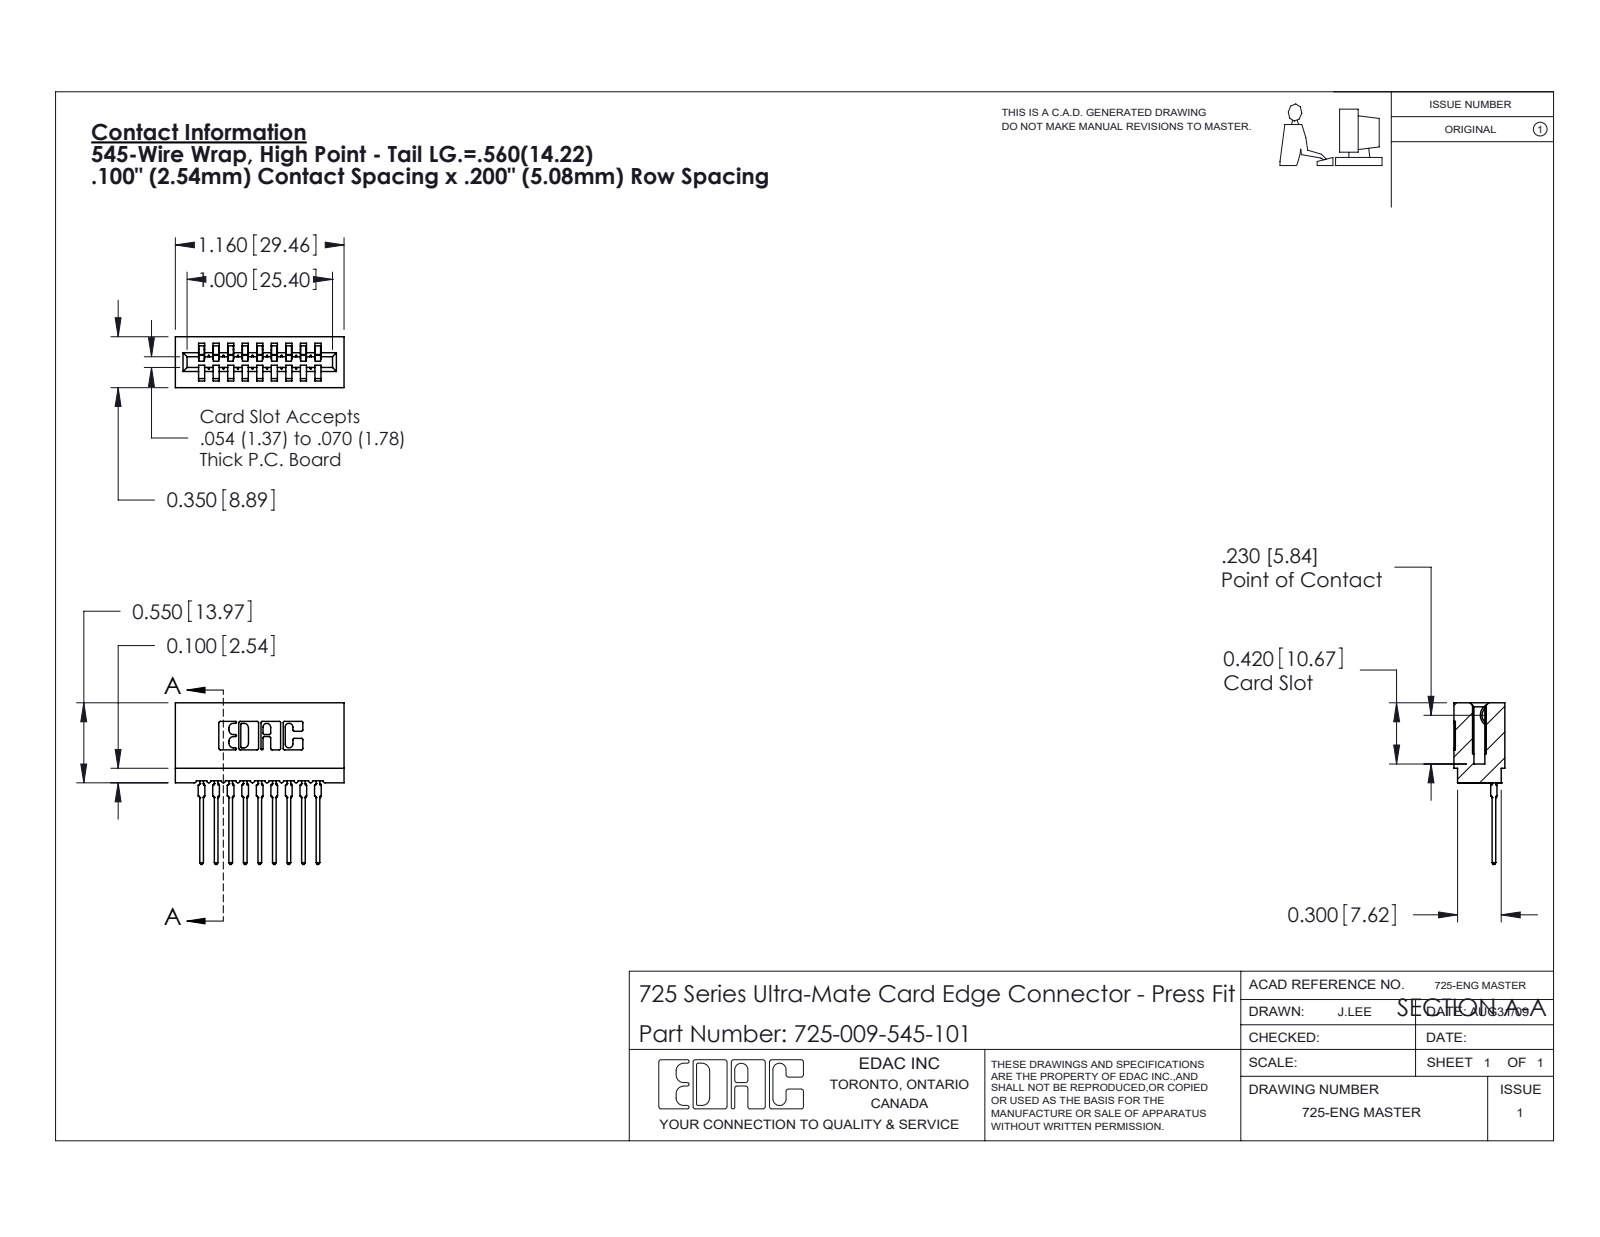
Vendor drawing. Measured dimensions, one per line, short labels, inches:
name: 725-009-545-101; 725 Part_Insulator Option - 01; 745-292-001_545
written by: SolidWorks 2020 (CONFIG_CONTROL_DESIGN)
unit: in
bodies: 10 solids, 1103 faces (658 planar, 211 cylindrical, 234 other)
size: 1.16 × 1.111 × 0.35
volume: 0.149 in³; area: 6.576 in²
rounds: 22× R0.01, 18× R0.015, 18× R0.021, 6× R0.007, 6× R0.031, 4× R0.005, 4× R0.011, 3× R0.026
face distances: 0.1, 0.2, 0.3, 0.4, 0.042, 0.5, 0.142, 0.058, 0.242, 0.158
